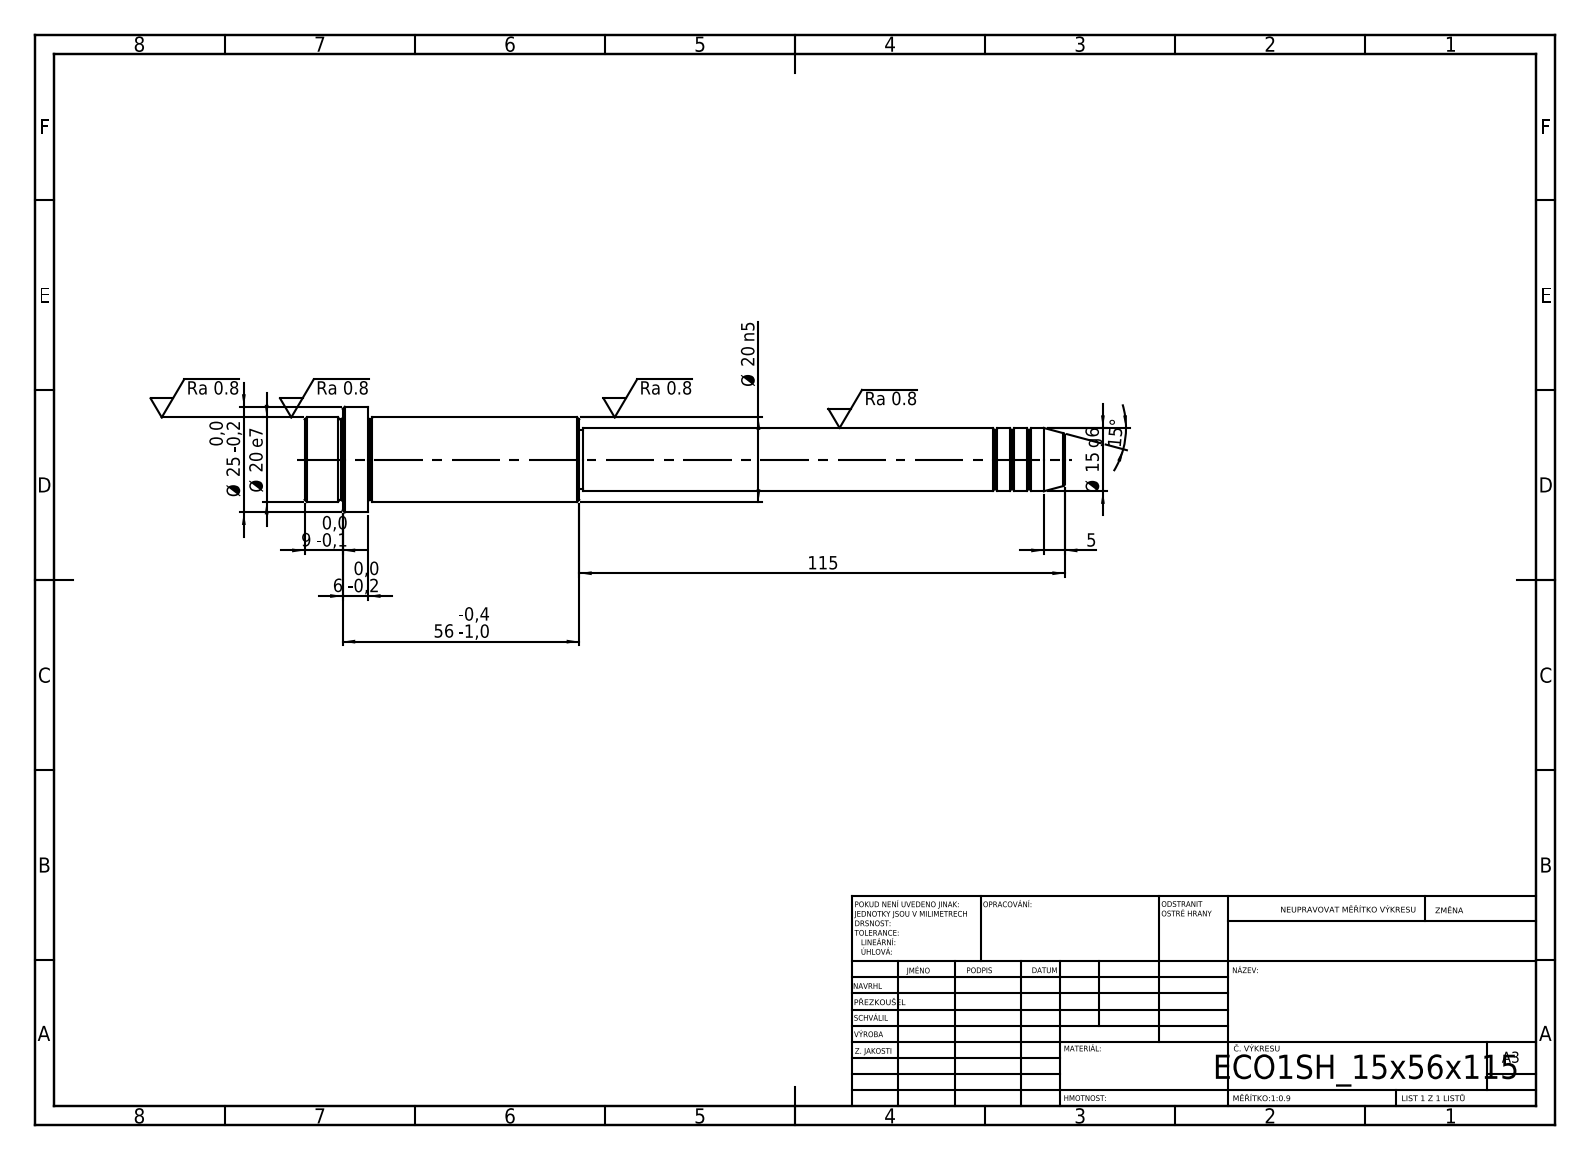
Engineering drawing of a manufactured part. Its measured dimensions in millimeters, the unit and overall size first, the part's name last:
Units: millimetres
Overall size (bounding box): 180 × 25 × 25
Round bosses / shafts (diameter × count): ⌀25 ×1, ⌀20 ×1, ⌀15 ×1, ⌀14 ×1
Main face-to-face distances: 15, 6, 9, 50, 56, 65, 115, 165, 171, 180
Volume: 41 503 mm³ · Surface area: 10 622 mm²
Bodies: 1 solid, 52 faces (6 planar, 16 cylindrical, 30 other)
STEP written by: SolidWorks 2019 (CONFIG_CONTROL_DESIGN)
